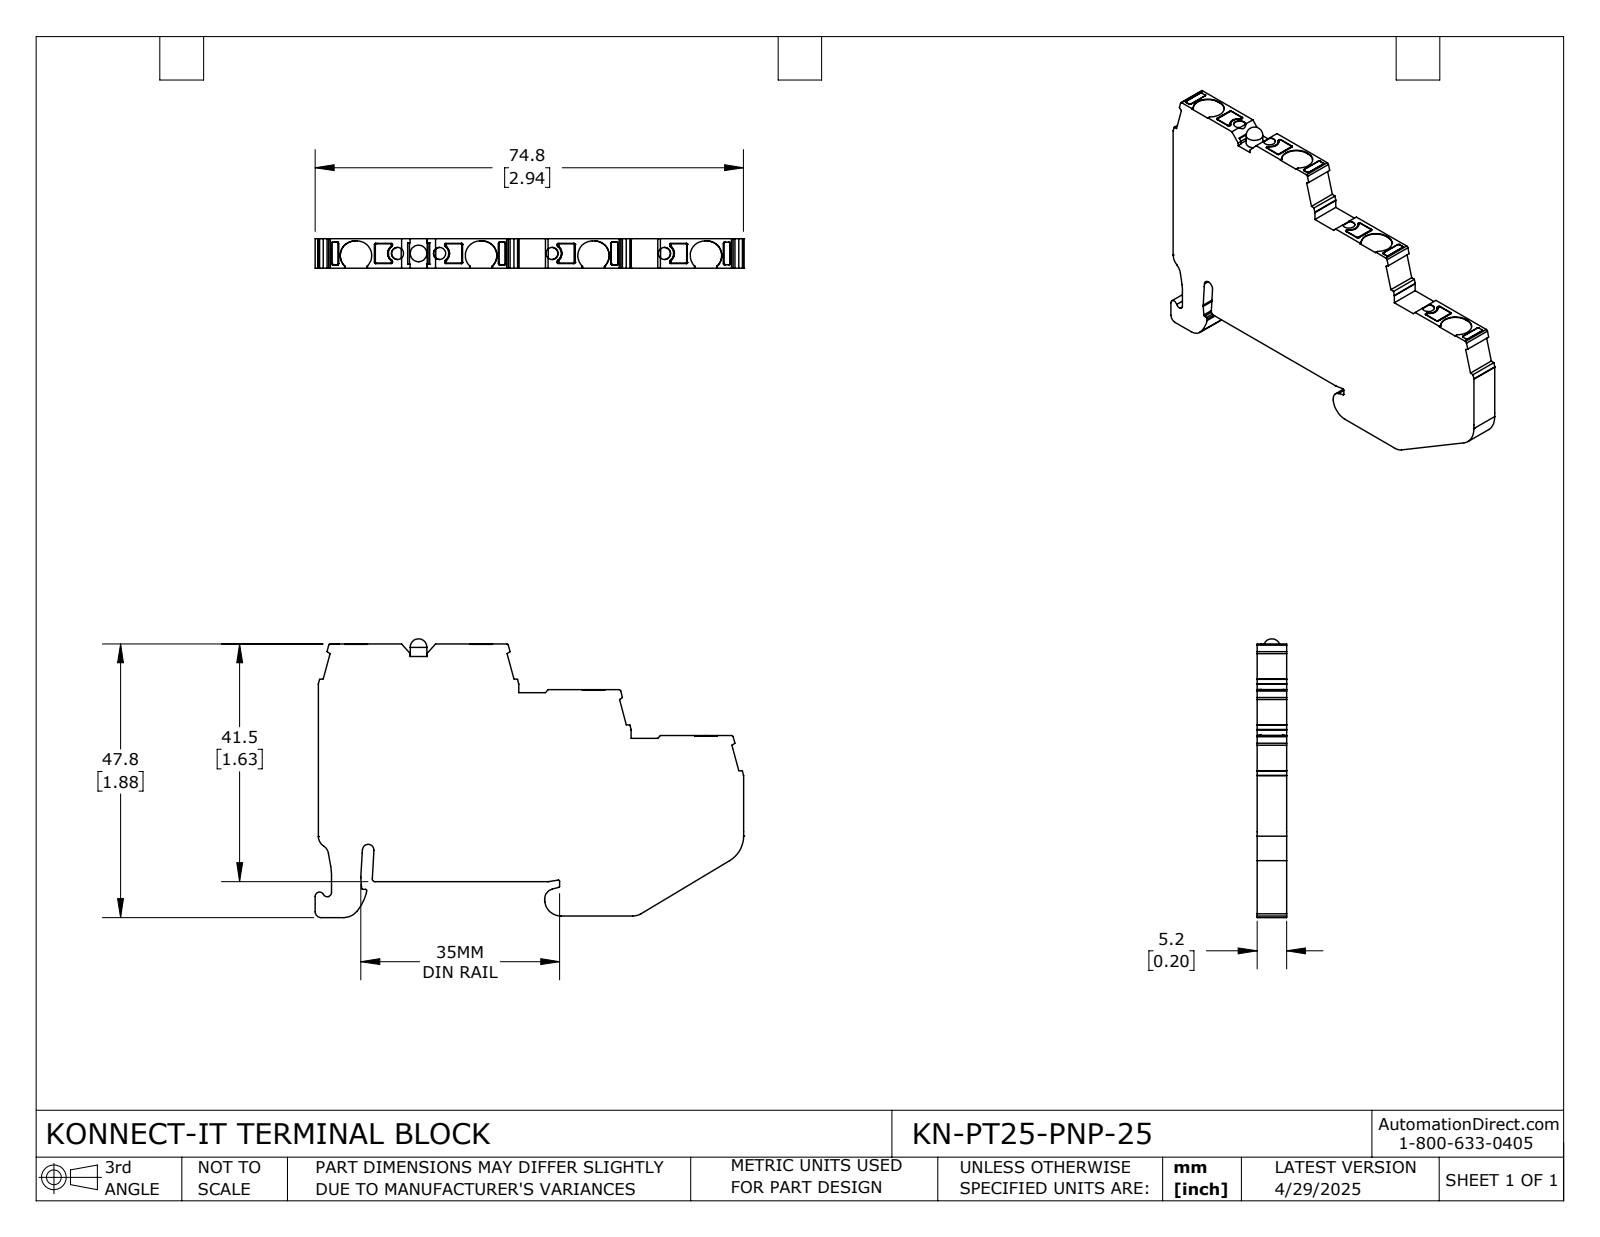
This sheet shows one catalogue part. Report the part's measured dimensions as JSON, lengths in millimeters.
{"part_name": "KN-PT25-PNP-25", "step_written_by": "SolidWorks 2024 (CONFIG_CONTROL_DESIGN)", "units": "millimeters", "bodies": {"solids": 1, "faces": 358, "planar": 201, "cylindrical": 146, "other": 11}, "overall_size": [74.8, 48.65, 5.15], "volume_mm3": 13781, "surface_area_mm2": 6772, "round_holes": [[2.1, 4]], "round_bosses_or_shafts": [[2.9, 1]], "partial_cylinders_radius": [[0.2, 68], [0.15, 16], [0.3, 8], [2.55, 8], [1.5, 4], [1.55, 4], [1, 3], [2, 3]], "face_to_face_distances": [5.15, 8, 6, 16, 7.99, 15.99, 74.25, 7.9, 8.1, 0.4], "hole_center_spacings": [7.34, 19.63, 19.64, 26.98, 39.27, 46.61]}
